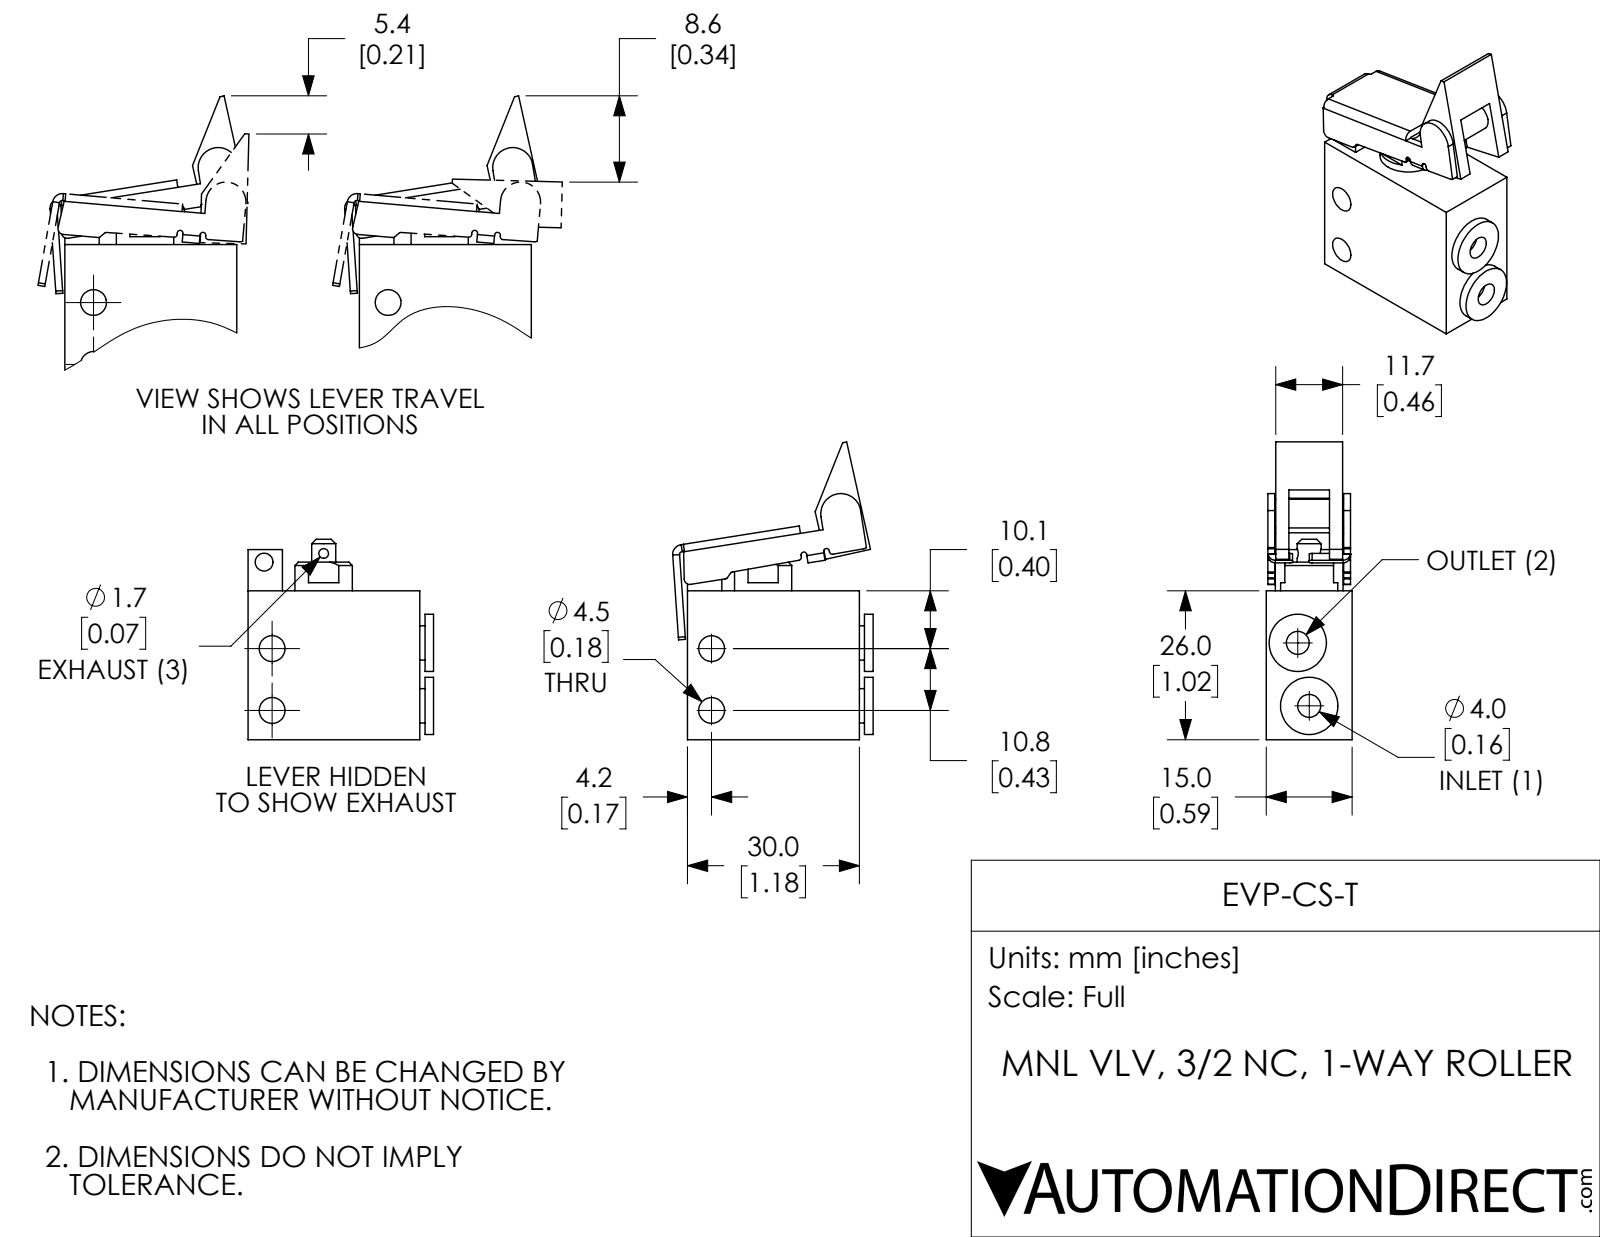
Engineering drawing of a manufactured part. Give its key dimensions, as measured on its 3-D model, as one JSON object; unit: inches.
{"part_name": "EVP-CS-T", "step_written_by": "SolidWorks 2017 (AUTOMOTIVE_DESIGN)", "units": "inches", "bodies": {"solids": 3, "faces": 154, "planar": 82, "cylindrical": 68, "other": 4}, "overall_size": [2.046, 1.378, 0.591], "volume_in3": 0.869, "surface_area_in2": 11.63, "round_holes": [[0.157, 3], [0.177, 2], [0.067, 1], [0.122, 1], [0.197, 1]], "round_bosses_or_shafts": [[0.394, 3], [0.236, 2], [0.165, 1]], "partial_cylinders_radius": [[0.02, 13], [0.051, 4], [0.004, 2], [0.016, 2], [0.039, 2], [0.067, 1], [0.138, 1]], "face_to_face_distances": [0.591, 0.047, 0.059, 0.579, 1.181, 0.531, 0.52, 1.024, 0.048, 0.065], "hole_center_spacings": [0.414, 0.425, 0.44, 0.597, 0.6, 0.743, 1.001, 1.021]}
